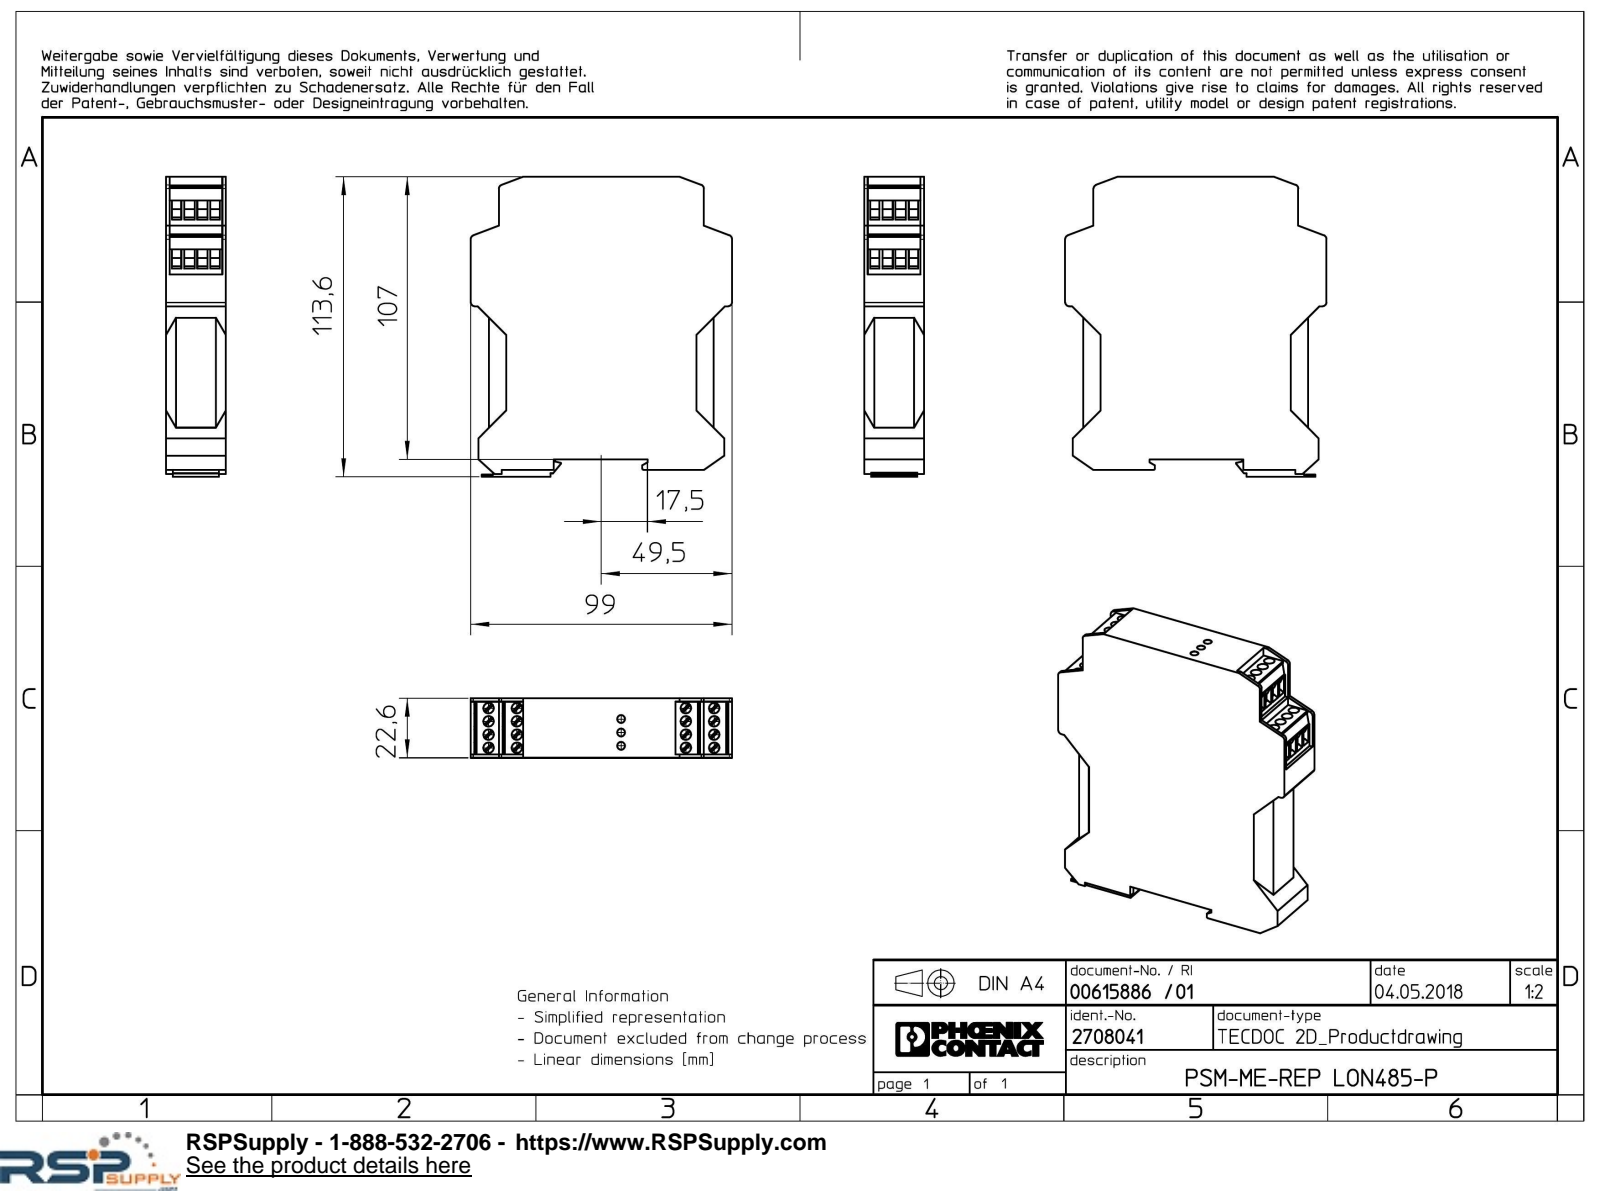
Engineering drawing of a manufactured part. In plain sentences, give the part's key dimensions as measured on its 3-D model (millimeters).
The part is named "PSM_ME_REP_LON485_P-select". Its 3-D file was written by "Creo Elements/Direct Modeling 18.1I 14-Aug-2016 (C) Parametric Technology GmbH (AUTOMOTIVE_DESIGN)". It is 1 solid with 353 faces: 296 planar, 57 cylindrical and 0 other. Overall it measures 113.6 by 99 by 22.6 millimeters. Its volume is 212 348 cubic millimeters and its surface area 30 417 square millimeters. Round holes: 16 of diameter 4, 3 of diameter 3. Partial cylindrical surfaces (rounded edges, fillets, slot ends): 8 of radius 0.2, 6 of radius 1.5, 1 of radius 0.5. The main face-to-face distances are 22.6, 4, 107, 85.1, 111, 6.95, 92.05, 10.7, 55.62, 18.5. The hole center spacings are 5, 11.81, 74.91, 10, 10.7, 14.65, 74.74, 75.41.
